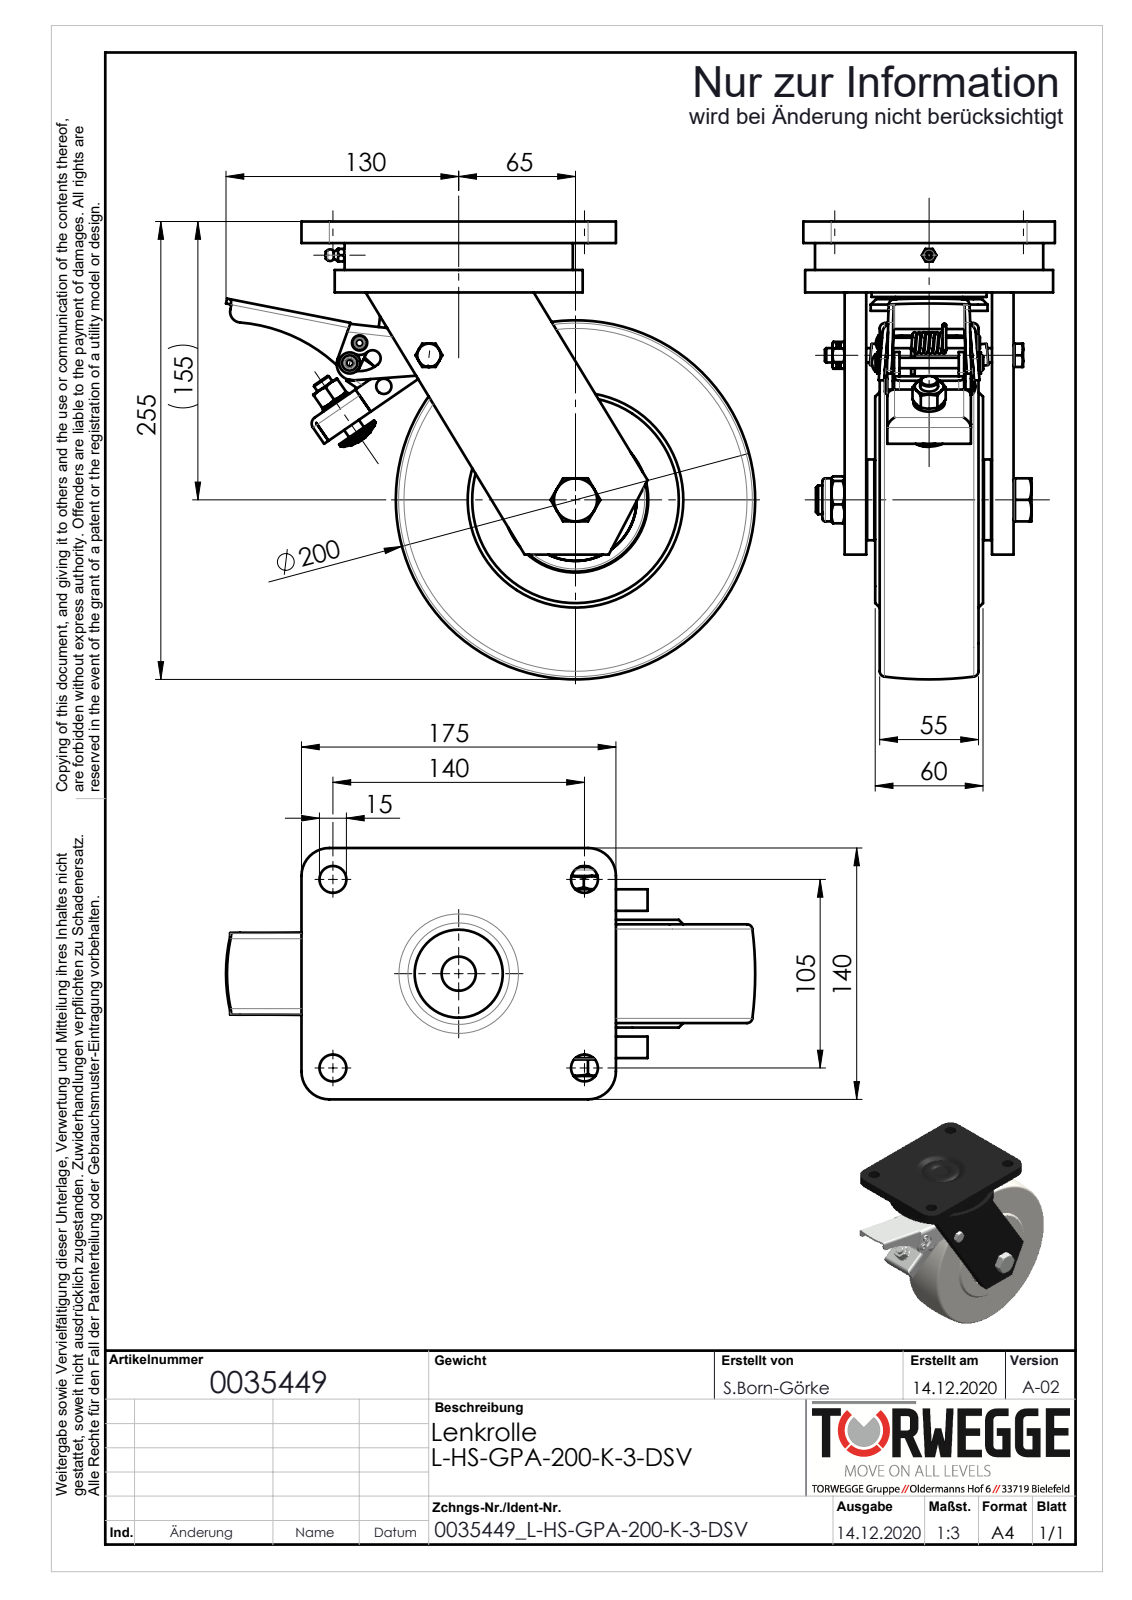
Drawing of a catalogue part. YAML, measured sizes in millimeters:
part_name: "0035449"
step_written_by: "SolidWorks 2018 (AUTOMOTIVE_DESIGN)"
units: millimeters
bodies: {solids: 51, faces: 926, planar: 287, cylindrical: 347, other: 292}
overall_size: [294.5, 255, 140]
volume: 2696000
surface_area: 485118
round_holes:
  - {diameter: 6, count: 7}
  - {diameter: 15, count: 4}
  - {diameter: 4, count: 3}
  - {diameter: 8.4, count: 2}
  - {diameter: 8.5, count: 2}
  - {diameter: 5, count: 1}
  - {diameter: 5.8, count: 1}
  - {diameter: 6.3, count: 1}
  - {diameter: 6.8, count: 1}
  - {diameter: 8, count: 1}
  - {diameter: 8.2, count: 1}
  - {diameter: 8.38, count: 1}
round_bosses_or_shafts:
  - {diameter: 12, count: 3}
  - {diameter: 8.5, count: 3}
  - {diameter: 24, count: 2}
  - {diameter: 6, count: 2}
  - {diameter: 5.8, count: 2}
  - {diameter: 2, count: 2}
  - {diameter: 138, count: 1}
  - {diameter: 127, count: 1}
partial_cylinders:
  - {radius: 4, count: 7}
  - {radius: 3, count: 4}
  - {radius: 4.25, count: 4}
  - {radius: 5.35, count: 4}
  - {radius: 15.5, count: 4}
  - {radius: 0.5, count: 3}
  - {radius: 6, count: 3}
  - {radius: 0.1, count: 2}
face_to_face_distances: [12, 7.5, 62.5, 19.5, 74.5, 82, 5, 2.5, 17, 77]
hole_center_spacings: [87.5, 12.43, 105, 140, 175, 23, 27.68, 30.5]
